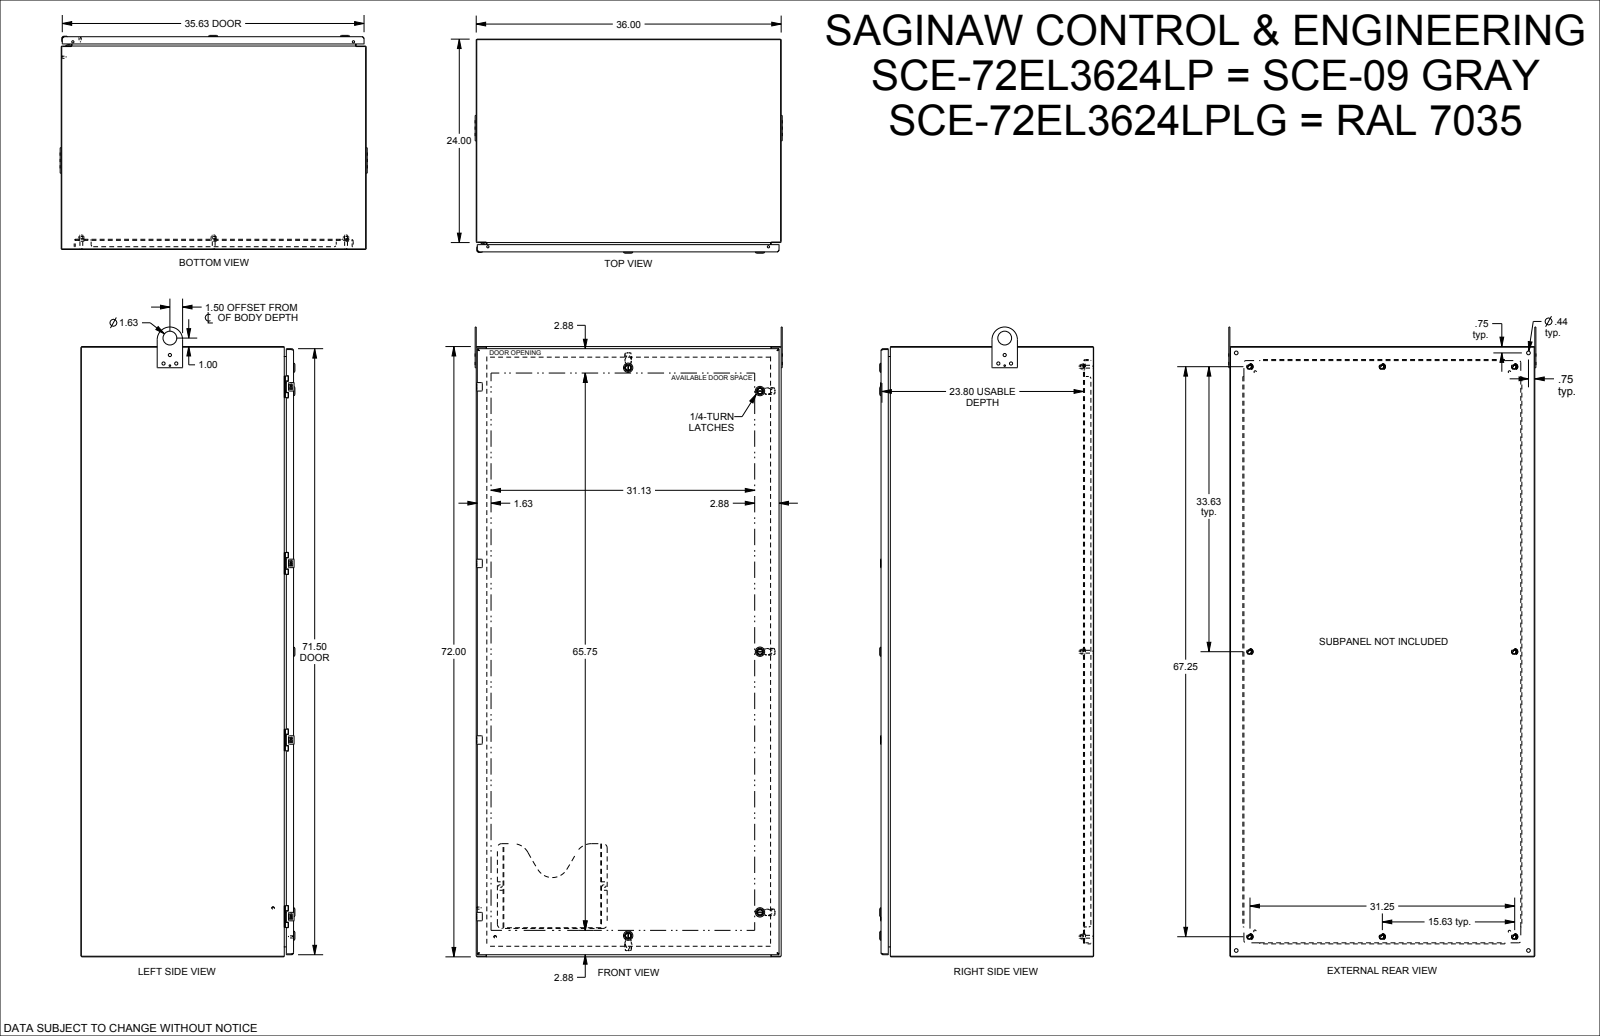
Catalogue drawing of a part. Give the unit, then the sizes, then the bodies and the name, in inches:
Units: inches
Overall size (bounding box): 74.31 × 36.262 × 25.256
Round holes (diameter × count): ⌀0.172 ×8, ⌀0.205 ×8, ⌀0.244 ×8, ⌀0.266 ×8, ⌀0.367 ×8, ⌀0.375 ×8, ⌀0.5 ×8, ⌀0.197 ×5, ⌀0.315 ×5, ⌀0.394 ×5, ⌀0.634 ×5, ⌀0.04 ×4
Round bosses / shafts (diameter × count): ⌀0.17 ×12, ⌀0.366 ×8, ⌀0.332 ×8, ⌀0.25 ×8, ⌀0.24 ×8, ⌀1.102 ×5, ⌀0.866 ×5, ⌀0.802 ×5
Partial cylindrical surfaces — rounded edges, fillets, slot ends (radius × count): R0.012 ×136, R0.01 ×70, R0.02 ×52, R0.015 ×42, R0.03 ×27, R0.025 ×20, R0.1 ×20, R0.157 ×20
Main face-to-face distances: 0.075, 0.075, 35.925, 0.104, 24.92, 24.995, 25.099, 25.024, 0.125, 1.125
Hole centre spacings: 20.833, 41.667, 20.833, 62.5, 0.05, 0.493, 0.494, 0.986
Bodies: 0 solids, 5593 faces (2661 planar, 1568 cylindrical, 1364 other)
Part name (STEP PRODUCT): SCE-72EL3624LPLG
STEP written by: SolidWorks 2019 (CONFIG_CONTROL_DESIGN)
